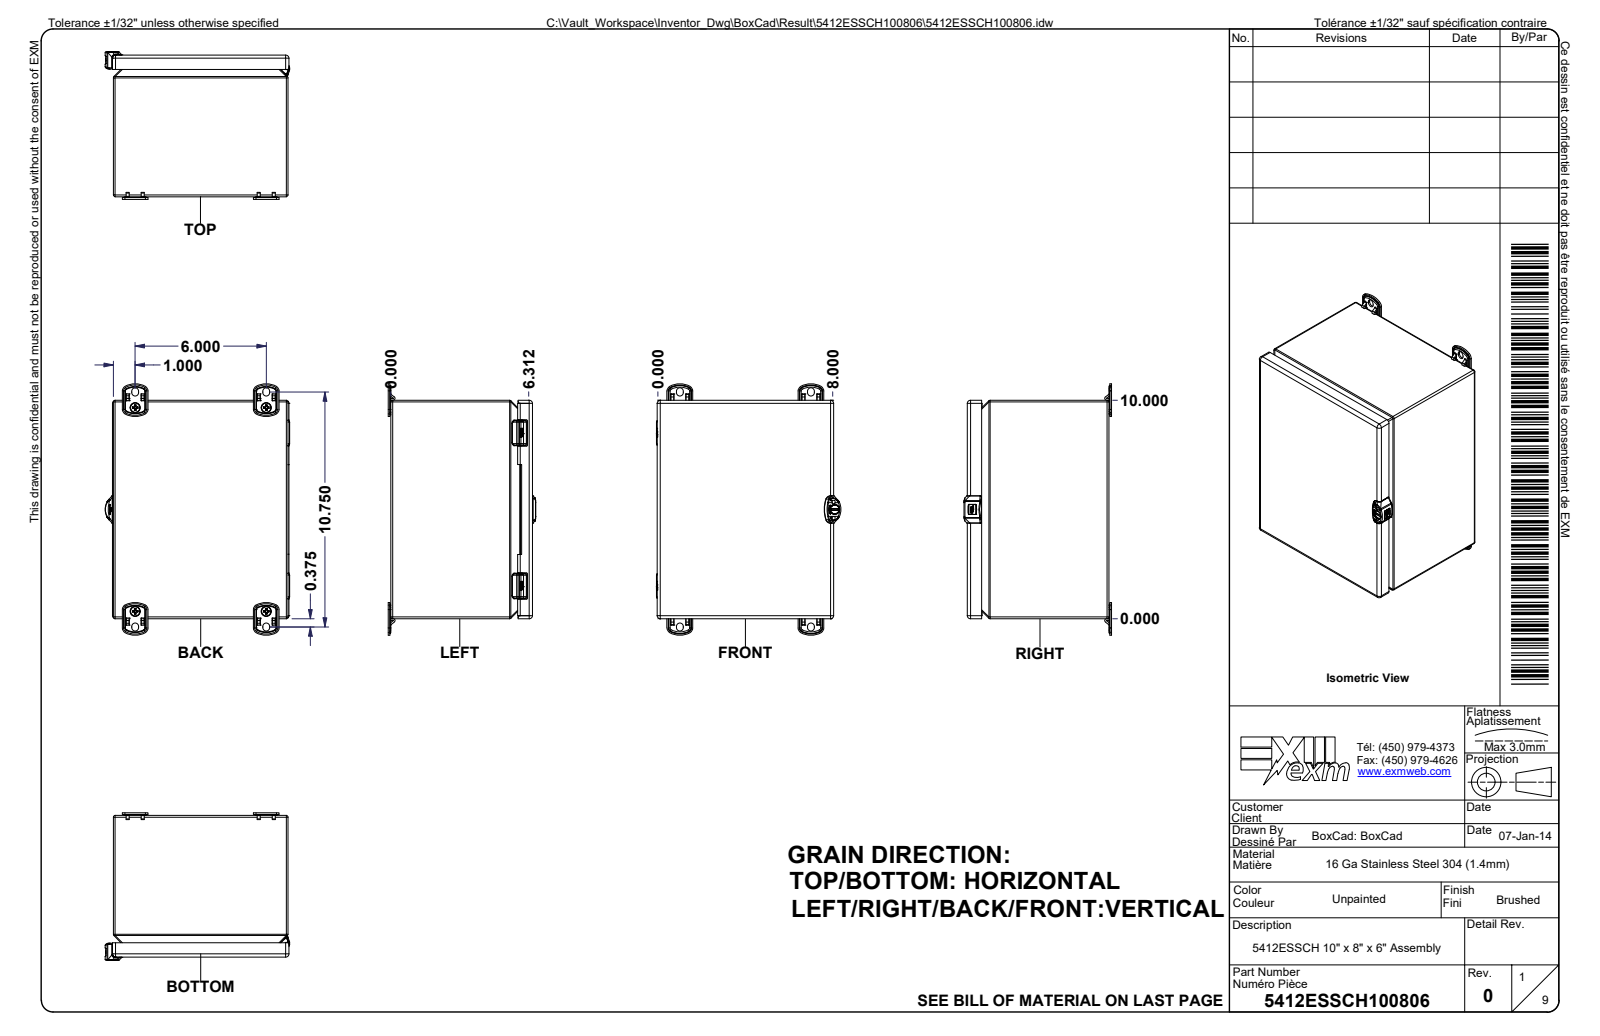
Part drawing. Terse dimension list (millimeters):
name: 5412ESSCH100806; 5412ESSCH100806B; 5412ESSCH100806B-P; STK-Q-08500 (+8 more)
written by: Autodesk Inventor 2024 (AUTOMOTIVE_DESIGN)
unit: mm
bodies: 44 solids, 6243 faces (3092 planar, 1251 cylindrical, 1900 other)
size: 292 × 214.4 × 171.6
volume: 482 100 mm³; area: 679 400 mm²
holes: 7× ⌀5.1, 6× ⌀0.8, 6× ⌀6.1, 4× ⌀5, 4× ⌀7.9, 4× ⌀8.1, 2× ⌀4.2, 2× ⌀4.4, 2× ⌀5.5, 2× ⌀6, 1× ⌀3.2, 1× ⌀10.7
bosses: 8× ⌀5.9, 6× ⌀10, 6× ⌀0.9, 4× ⌀13, 4× ⌀12.7, 3× ⌀5, 2× ⌀7.6, 2× ⌀4.9
rounds: 185× R0.2, 85× R0.5, 63× R0.1, 61× R0.3, 42× R0.3, 42× R1, 32× R0.8, 25× R1.5
face distances: 1.3, 163.3, 201.9, 252.7, 161.9, 164.6, 11.4, 151.9, 153.3, 10
hole spacings: 262.9, 13.9, 158.8, 223, 271.9, 156.2, 209.6, 209.6
